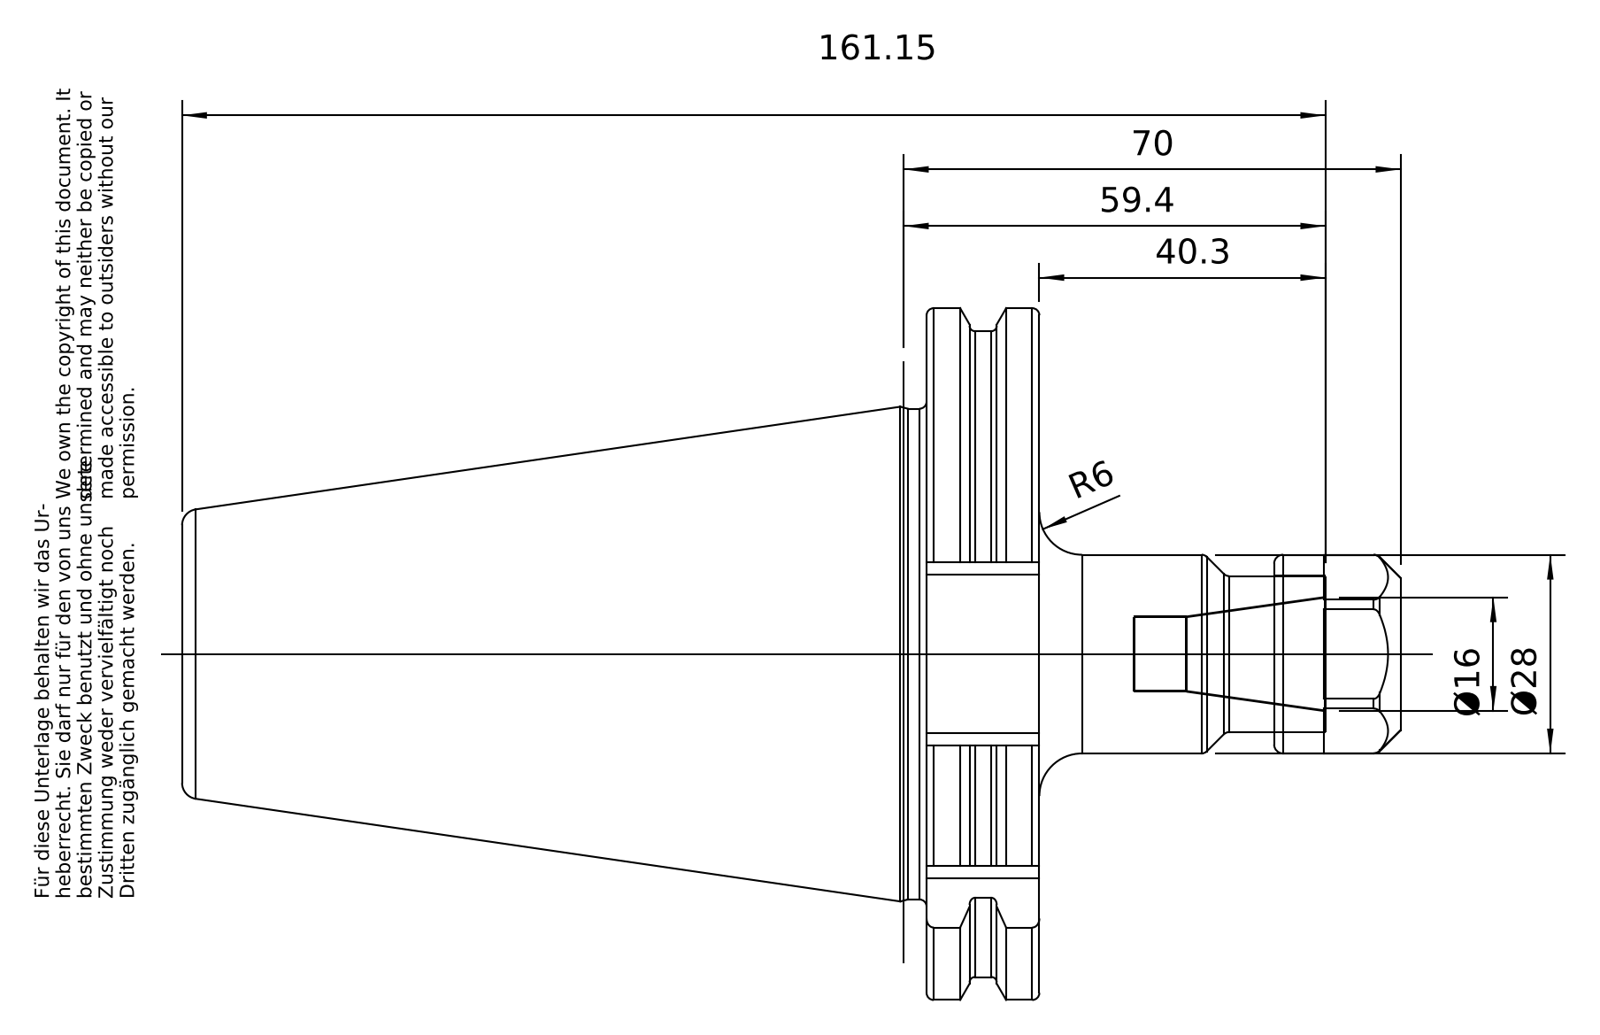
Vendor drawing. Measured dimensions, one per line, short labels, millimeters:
name: 50-320-16; 83-912-16; 50-320-16_ASM
written by: PRO/ENGINEER BY PARAMETRIC TECHNOLOGY CORPORATION, 2010430 (CONFIG_CONTROL_DESIGN)
unit: mm
bodies: 2 solids, 129 faces (29 planar, 32 cylindrical, 68 other)
size: 171.6 × 97.47 × 94
volume: 367 825 mm³; area: 49 035 mm²
holes: 1× ⌀10.5, 1× ⌀20.75, 1× ⌀25.01, 1× ⌀25.7
bosses: 1× ⌀91, 1× ⌀69.15, 1× ⌀28, 1× ⌀24.01, 1× ⌀22
rounds: 5× R1.75, 1× R48.74
face distances: 15.85, 49, 33.15, 104.8, 120.65, 153.8, 25, 171.6, 66.8, 50.95
